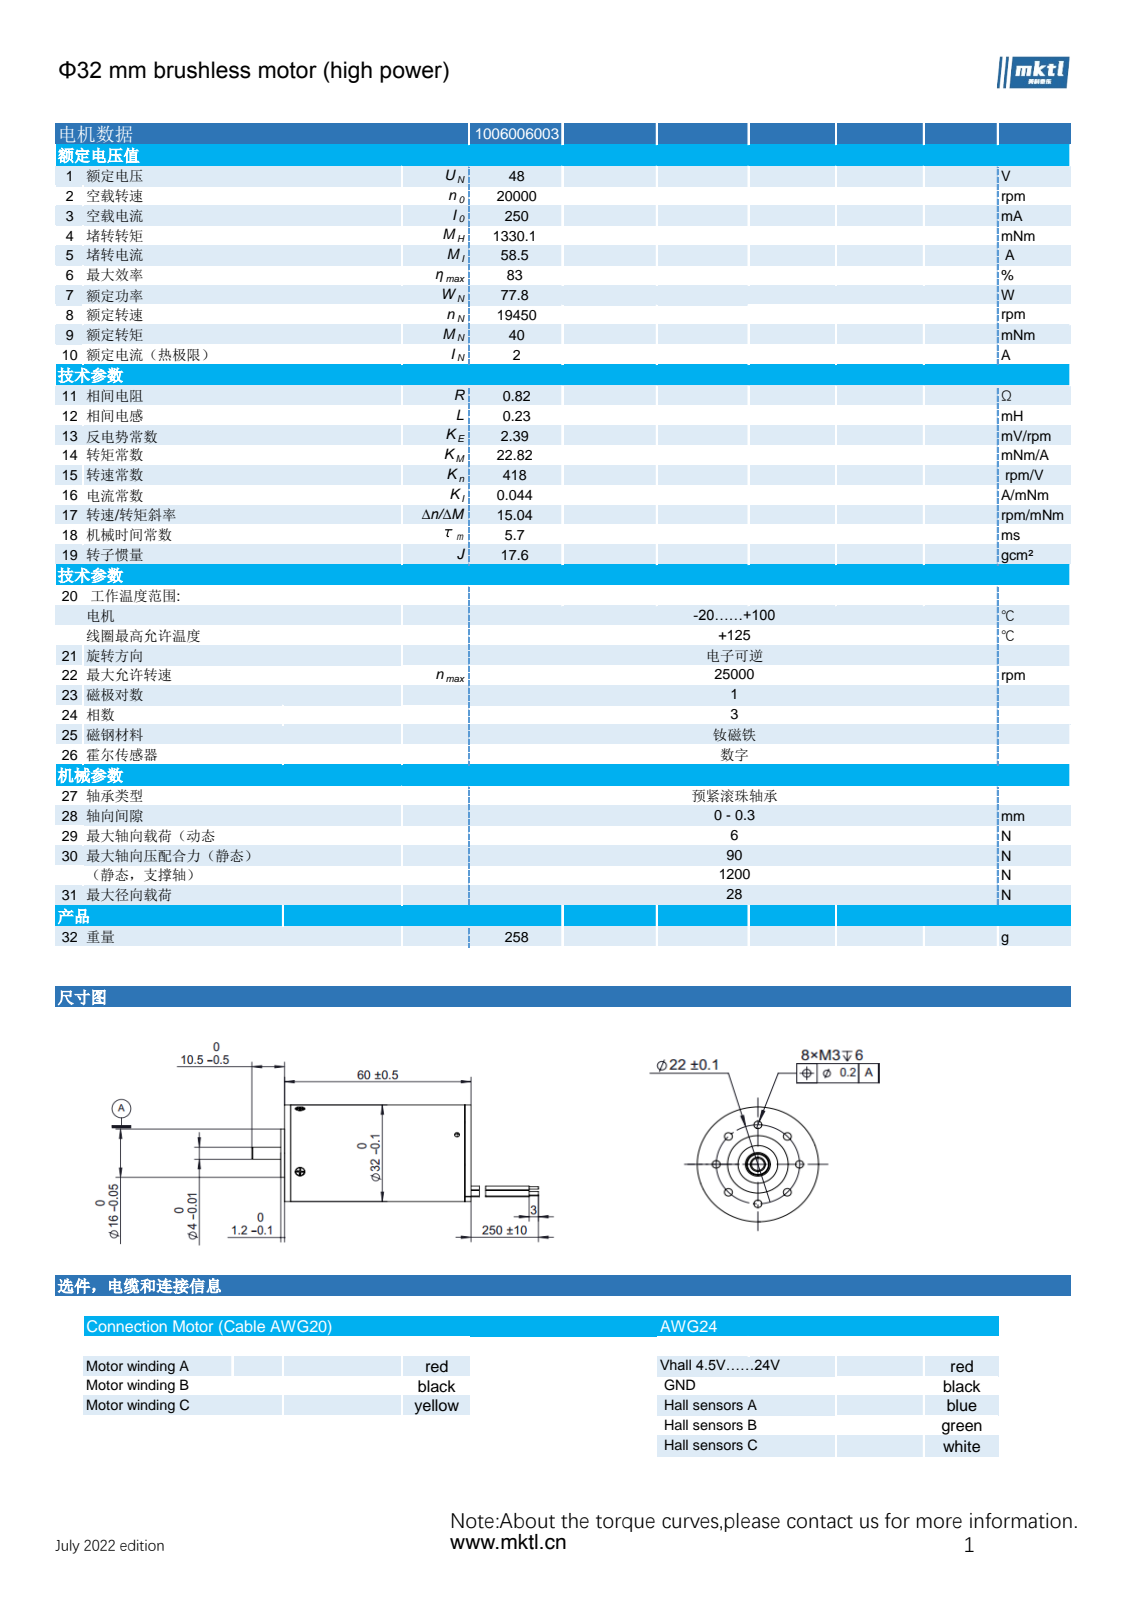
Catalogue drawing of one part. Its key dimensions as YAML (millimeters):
part_name: "approval 106006003"
step_written_by: "SolidWorks 2025 (AUTOMOTIVE_DESIGN)"
units: millimeters
bodies: {solids: 264, faces: 2548, planar: 930, cylindrical: 1511, other: 107}
overall_size: [92.18, 32, 32]
volume: 40911
surface_area: 148161
round_holes:
  - {diameter: 2.1, count: 11}
  - {diameter: 1.1, count: 5}
  - {diameter: 1.5, count: 5}
  - {diameter: 0.5, count: 4}
  - {diameter: 1.25, count: 4}
  - {diameter: 3.1, count: 4}
  - {diameter: 1.2, count: 3}
  - {diameter: 3, count: 3}
  - {diameter: 1.6, count: 2}
  - {diameter: 1.3, count: 1}
  - {diameter: 6, count: 1}
  - {diameter: 9, count: 1}
round_bosses_or_shafts:
  - {diameter: 1.4, count: 7}
  - {diameter: 1.2, count: 5}
  - {diameter: 0.8, count: 5}
  - {diameter: 4, count: 4}
  - {diameter: 2.8, count: 4}
  - {diameter: 1.6, count: 4}
  - {diameter: 1.3, count: 4}
  - {diameter: 1.8, count: 3}
partial_cylinders:
  - {radius: 0.1, count: 24}
  - {radius: 0.3, count: 21}
  - {radius: 0.75, count: 11}
  - {radius: 0.2, count: 5}
  - {radius: 1.5, count: 4}
  - {radius: 8, count: 2}
  - {radius: 6, count: 1}
  - {radius: 7.5, count: 1}
face_to_face_distances: [0.6, 0.4, 0.8, 1, 1.2, 1.4, 1.6, 1.8, 37, 2]
hole_center_spacings: [8.42, 11, 15.56, 20.33, 2, 12.25, 22.7, 23.62]
